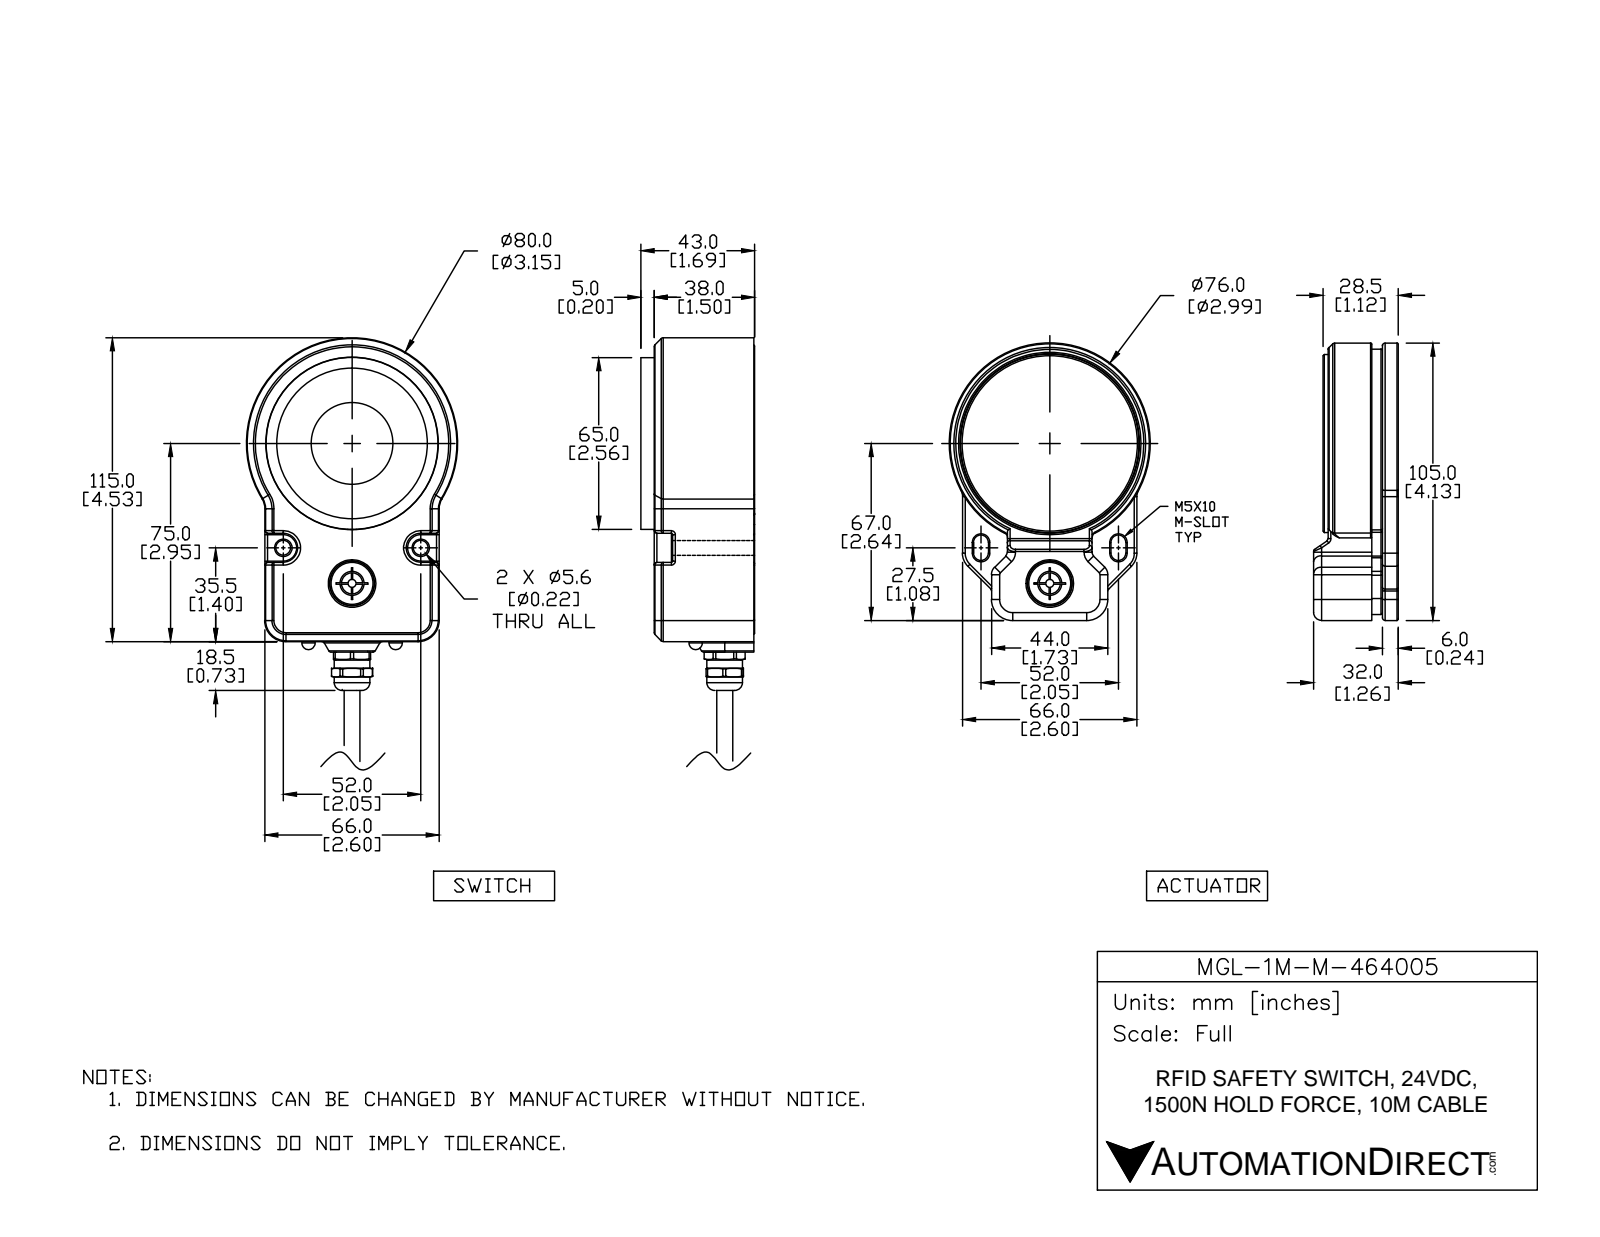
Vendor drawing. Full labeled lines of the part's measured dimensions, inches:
Part name (STEP PRODUCT): MGL-1M-M-464005_1; MGL-1M-M-464005_2; MGL-1M-M-464005
STEP written by: SolidWorks 2017 (AUTOMOTIVE_DESIGN)
Units: inches
Bodies: 19 solids, 1753 faces (428 planar, 743 cylindrical, 582 other)
Overall size (bounding box): 8.163 × 3.15 × 2.85
Volume: 19.31 in³ · Surface area: 219.5 in²
Round holes (diameter × count): ⌀0.098 ×8, ⌀0.13 ×6, ⌀0.197 ×6, ⌀0.453 ×5, ⌀0.157 ×3, ⌀0.315 ×3, ⌀0.354 ×3, ⌀0.22 ×2, ⌀0.276 ×2, ⌀0.374 ×2, ⌀0.465 ×2, ⌀0.252 ×1
Round bosses / shafts (diameter × count): ⌀0.02 ×4, ⌀0.079 ×3, ⌀0.472 ×2, ⌀0.228 ×2, ⌀0.213 ×2, ⌀0.047 ×2, ⌀2.992 ×1, ⌀2.811 ×1
Partial cylindrical surfaces — rounded edges, fillets, slot ends (radius × count): R0.02 ×186, R0.039 ×86, R0.079 ×26, R0.012 ×17, R0.118 ×13, R0.157 ×9, R0.217 ×8, R0.024 ×7
Main face-to-face distances: 0.315, 0.236, 2.299, 1.378, 0.118, 2.614, 0.413, 2.201, 2.85, 0.65
Hole centre spacings: 1.392, 1.969, 0.984, 1.28, 1.537, 0.787, 1.364, 0.349
